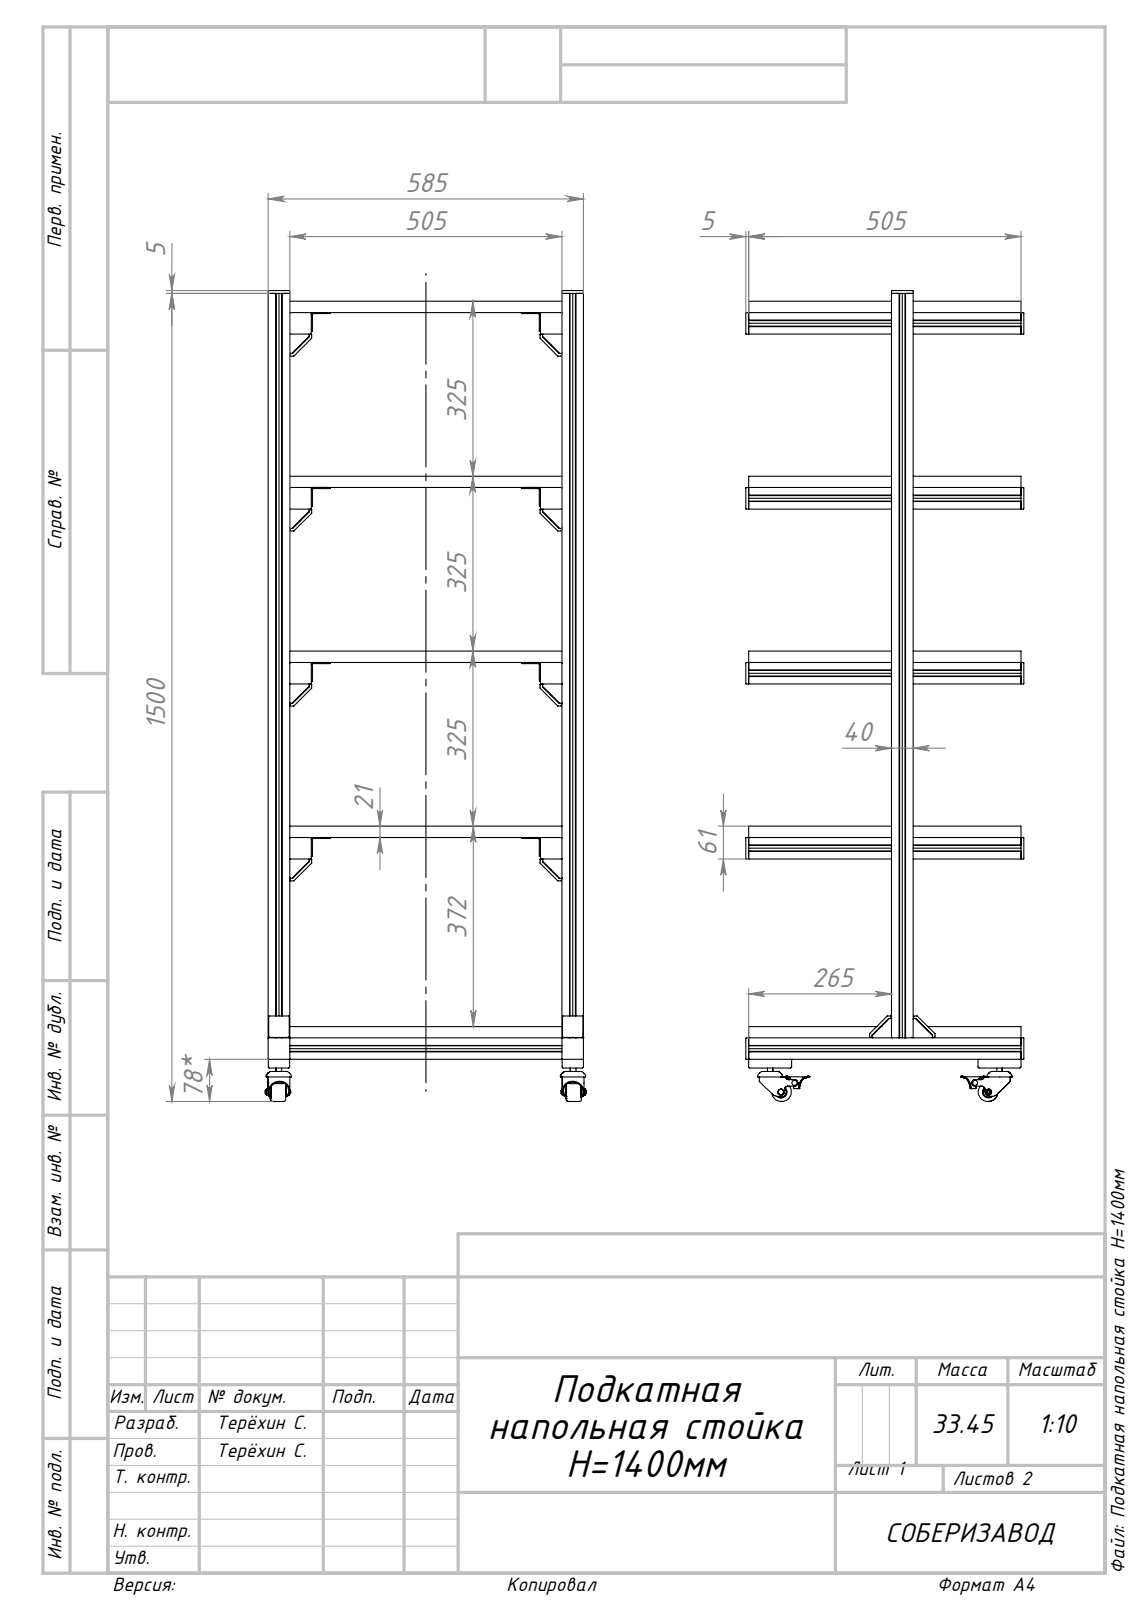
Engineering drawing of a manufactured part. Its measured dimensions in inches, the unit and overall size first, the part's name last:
Units: inches
Overall size (bounding box): 59.264 × 23.465 × 20.299
Round holes (diameter × count): ⌀0.067 ×48, ⌀0.197 ×24, ⌀0.319 ×18, ⌀0.236 ×16, ⌀0.354 ×8, ⌀0.394 ×8, ⌀0.591 ×8, ⌀0.854 ×8, ⌀0.335 ×4, ⌀0.472 ×4, ⌀0.646 ×4, ⌀0.866 ×4
Round bosses / shafts (diameter × count): ⌀0.197 ×20, ⌀0.787 ×8, ⌀0.224 ×8, ⌀1.378 ×4, ⌀0.63 ×4, ⌀0.394 ×4
Partial cylindrical surfaces — rounded edges, fillets, slot ends (radius × count): R0.039 ×1322, R0.01 ×1072, R0.012 ×336, R0.02 ×128, R0.014 ×112, R0.024 ×112, R0.031 ×112, R0.079 ×92
Main face-to-face distances: 0.827, 12.786, 25.572, 14.646, 27.432, 40.218, 53.004, 38.358, 12.786, 1.575
Hole centre spacings: 1.181, 13.622, 1.67, 13.622, 21.457, 12.786, 0.547, 0.956
Volume: 1 987 in³ · Surface area: 12 300 in²
Bodies: 141 solids, 11972 faces (6240 planar, 4736 cylindrical, 996 other)
Part name (STEP PRODUCT): 40õ40SL_1; T25_00; Фанера5; Фанера4 (+8 more)
STEP written by: SolidWorks 2021 (AUTOMOTIVE_DESIGN)
